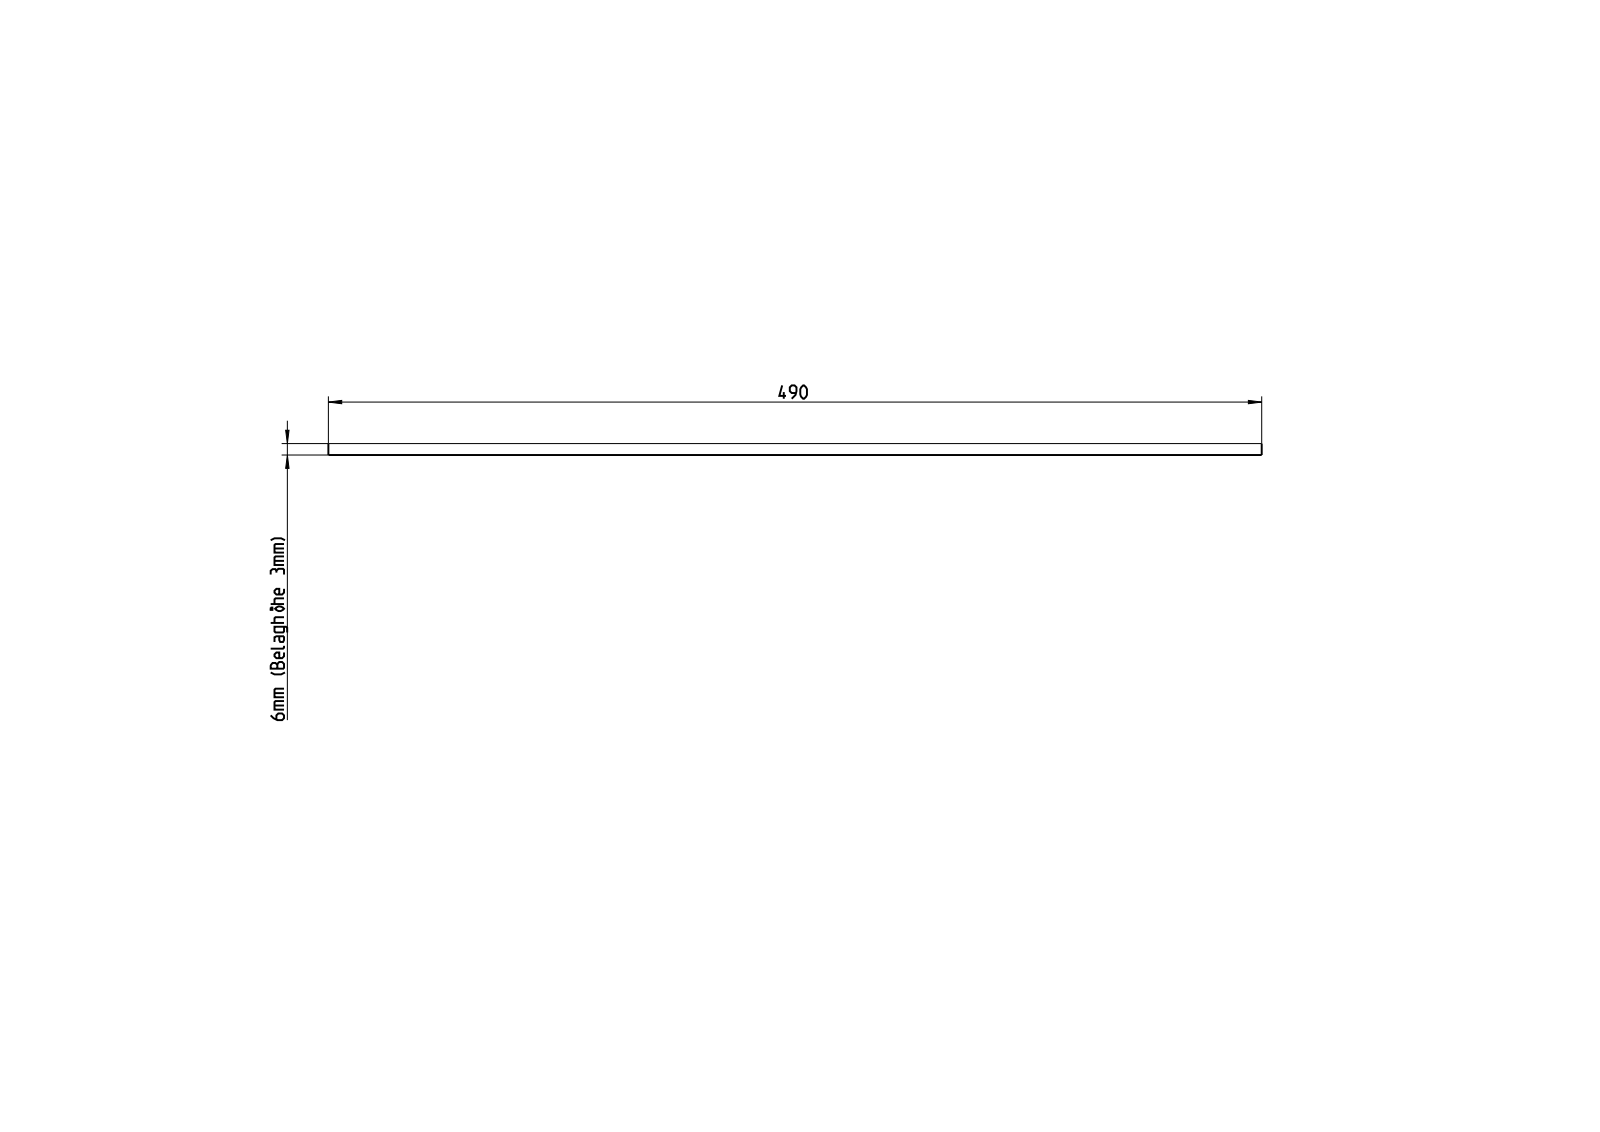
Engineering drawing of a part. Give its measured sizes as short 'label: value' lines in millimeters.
name: BKG5002W3; BKG5002W3_ASM
written by: CREO PARAMETRIC BY PTC INC, 2022024 (AUTOMOTIVE_DESIGN)
unit: mm
bodies: 1 solid, 6 faces (6 planar, 0 cylindrical, 0 other)
size: 999 × 490 × 6
volume: 2 937 000 mm³; area: 996 888 mm²
face distances: 6, 490, 999
